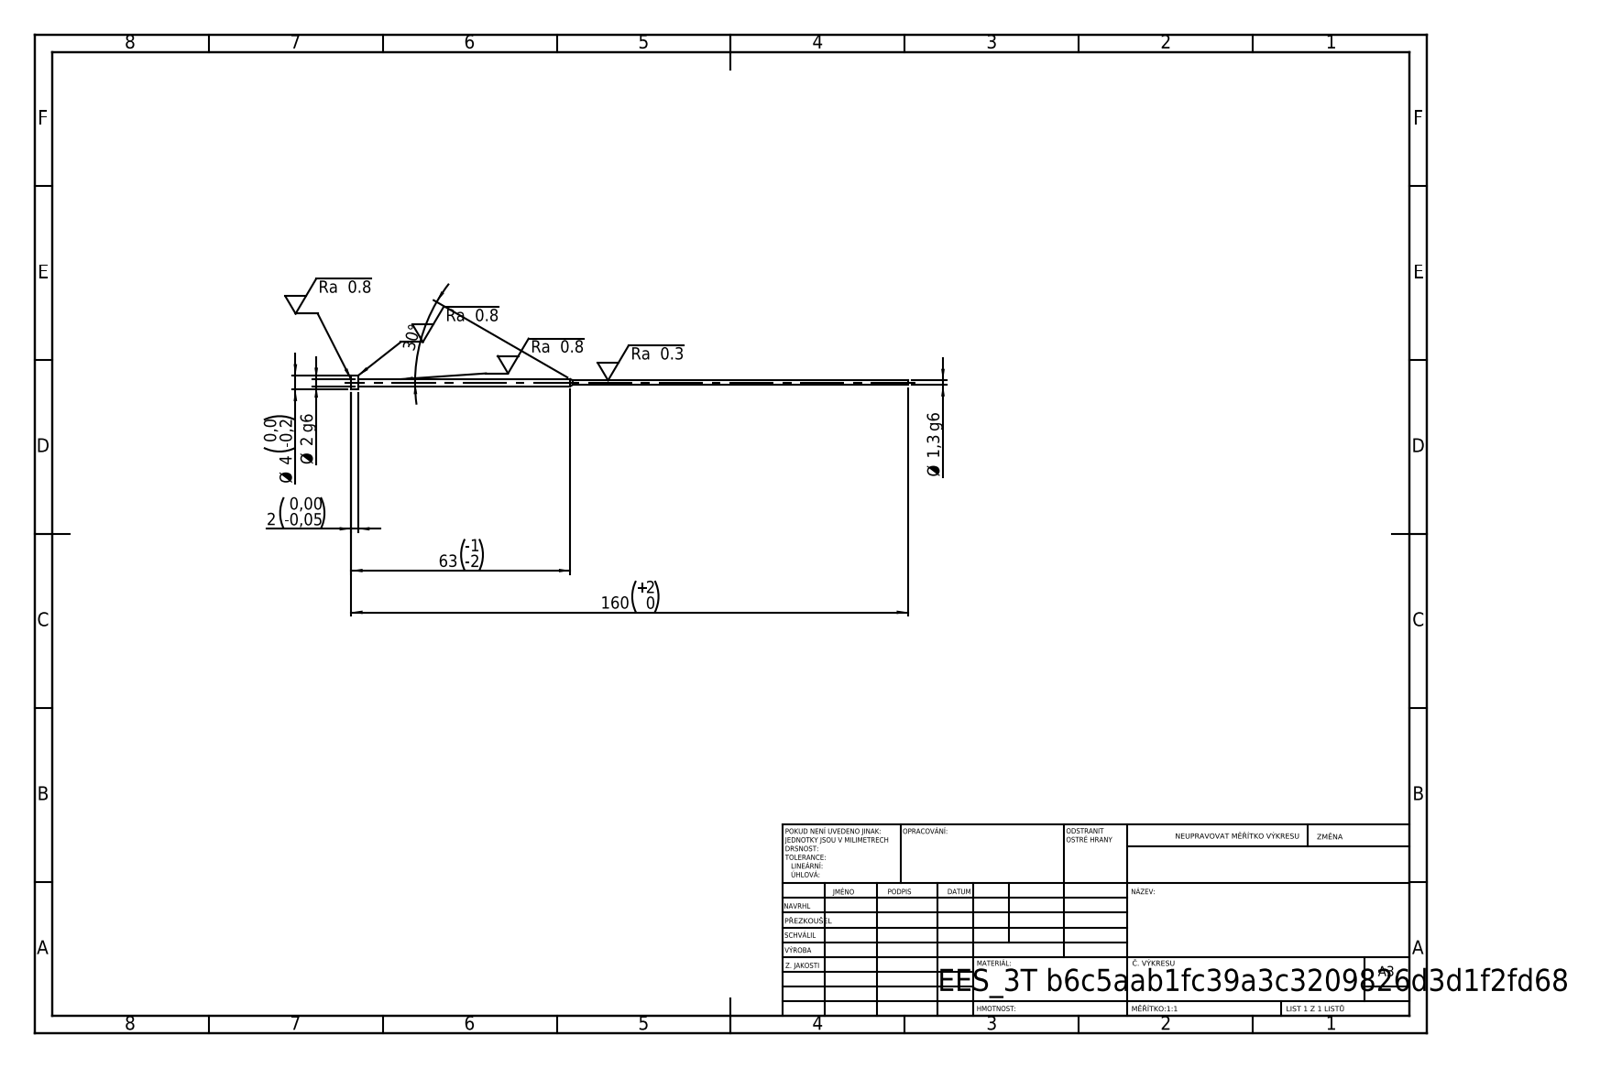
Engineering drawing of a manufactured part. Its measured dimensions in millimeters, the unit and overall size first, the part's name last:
Units: millimetres
Overall size (bounding box): 160 × 4 × 4
Round bosses / shafts (diameter × count): ⌀4 ×1, ⌀2 ×1, ⌀1.3 ×1
Main face-to-face distances: 2, 158, 160
Volume: 346 mm³ · Surface area: 829 mm²
Bodies: 1 solid, 11 faces (3 planar, 6 cylindrical, 2 other)
STEP written by: SolidWorks 2019 (CONFIG_CONTROL_DESIGN)
